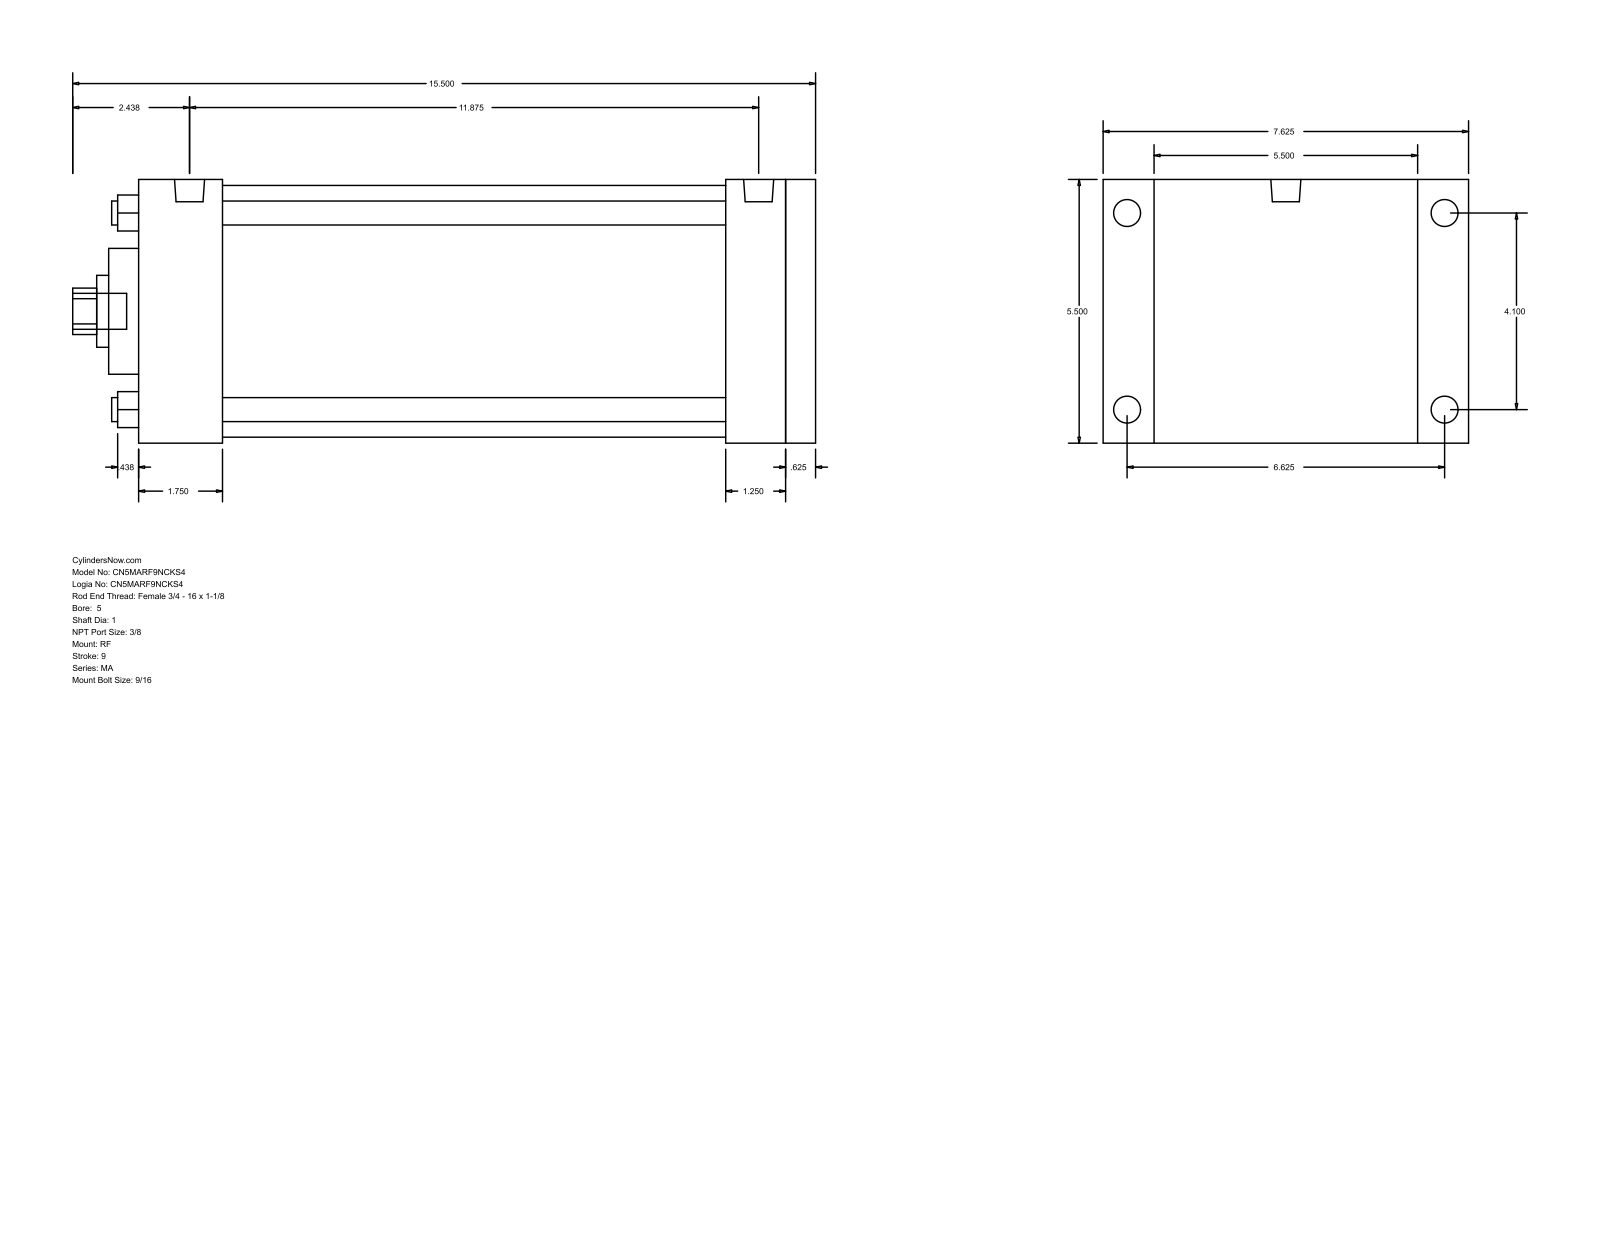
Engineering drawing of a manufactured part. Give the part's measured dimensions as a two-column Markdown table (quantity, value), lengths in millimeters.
| quantity | value |
| --- | --- |
| part name | MA_RF__0500_1 |
| STEP written by | GSSL Pune (CONFIG_CONTROL_DESIGN) |
| units | millimeters |
| bodies | 0 solids, 94 faces (65 planar, 29 cylindrical, 0 other) |
| overall size | 393.7 × 193.68 × 139.7 |
| round holes (diameter × count) | 12.7 × 4, 25.4 × 1, 38.1 × 1, 66.67 × 1, 133.35 × 1 |
| round bosses / shafts (diameter × count) | 14.29 × 4, 11.11 × 4, 15.93 × 2, 19.05 × 1 |
| partial cylindrical surfaces (radius × count) | 12.29 × 1 |
| main face-to-face distances | 139.7, 358.78, 342.9, 15.88, 44.46, 298.44, 314.32, 311.15, 266.69, 31.75 |
| hole center spacings | 73.64, 104.14, 147.28 |
